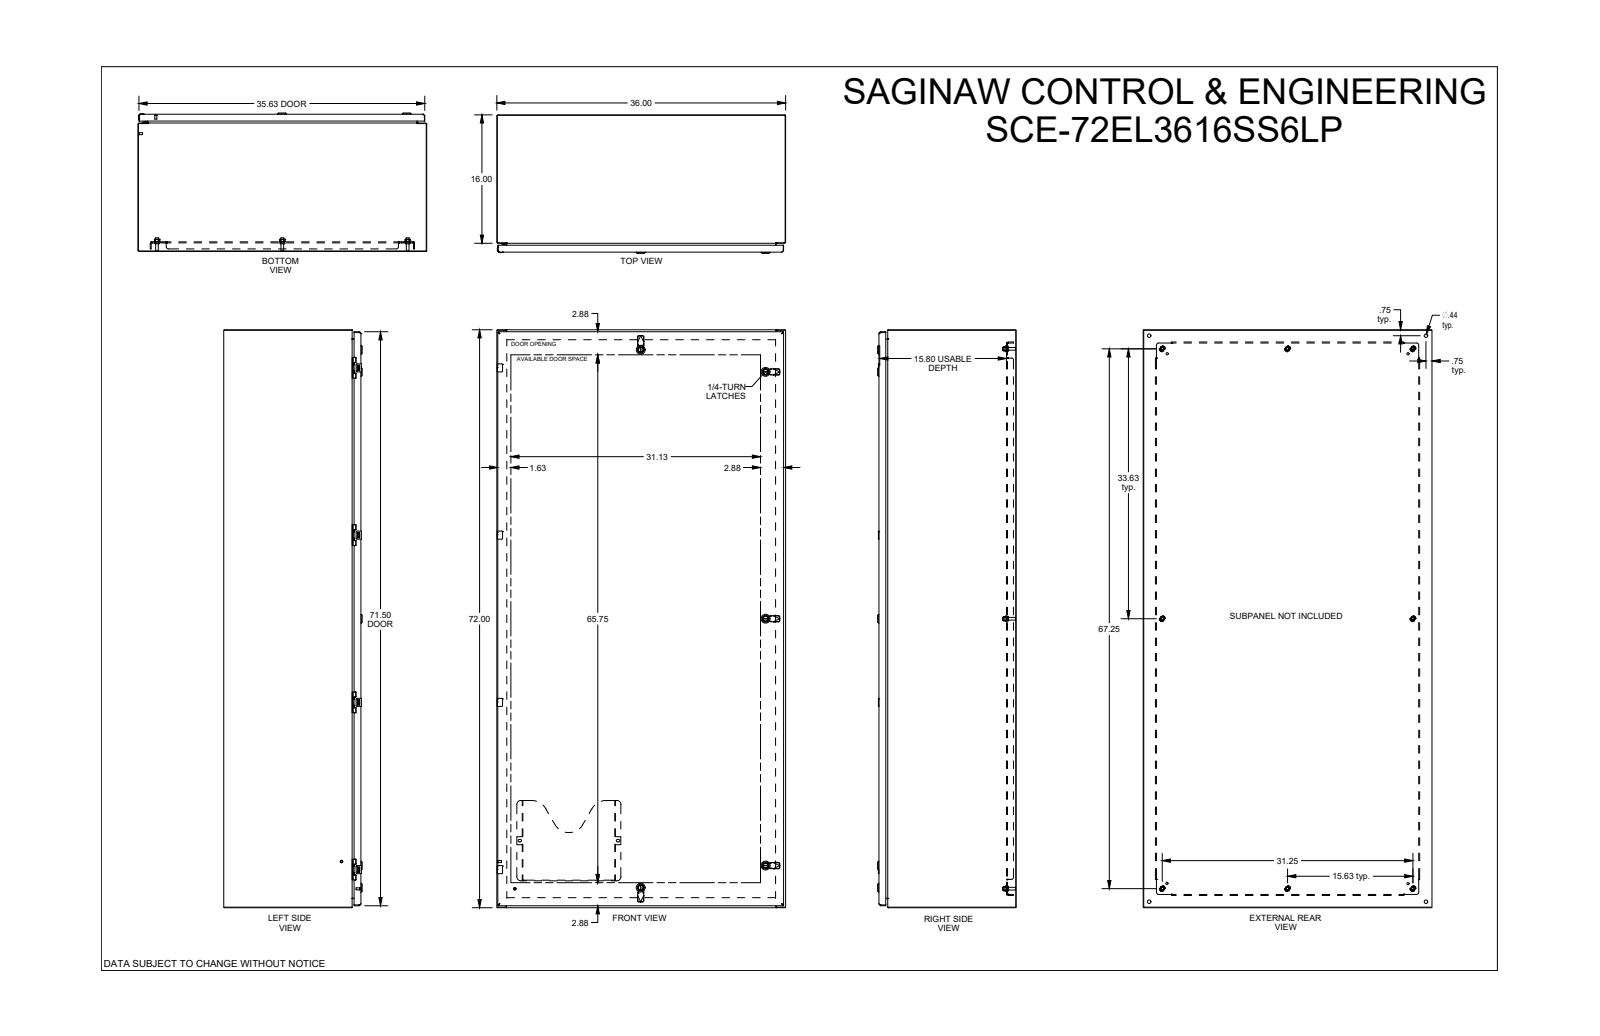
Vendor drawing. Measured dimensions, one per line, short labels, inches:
name: SCE-72EL3616SS6LP
written by: SolidWorks 2019 (CONFIG_CONTROL_DESIGN)
unit: in
bodies: 0 solids, 5420 faces (2661 planar, 1535 cylindrical, 1224 other)
size: 72 × 36 × 17.256
holes: 15× ⌀0.394, 8× ⌀0.172, 8× ⌀0.205, 8× ⌀0.244, 8× ⌀0.266, 8× ⌀0.367, 8× ⌀0.375, 8× ⌀0.5, 5× ⌀0.197, 5× ⌀0.315, 5× ⌀0.634, 4× ⌀0.156
bosses: 12× ⌀0.17, 8× ⌀0.366, 8× ⌀0.332, 8× ⌀0.25, 5× ⌀1.102, 5× ⌀0.866, 5× ⌀0.802, 5× ⌀0.78
rounds: 142× R0.012, 52× R0.01, 52× R0.02, 48× R0.015, 23× R0.04, 20× R0.157, 17× R0.03, 16× R0.031
face distances: 0.075, 0.104, 16.995, 16.92, 1, 17.099, 17.024, 0.075, 1.125, 15.795
hole spacings: 2.461, 20.833, 41.667, 1.274, 4.754, 3.48, 4.262, 20.833
